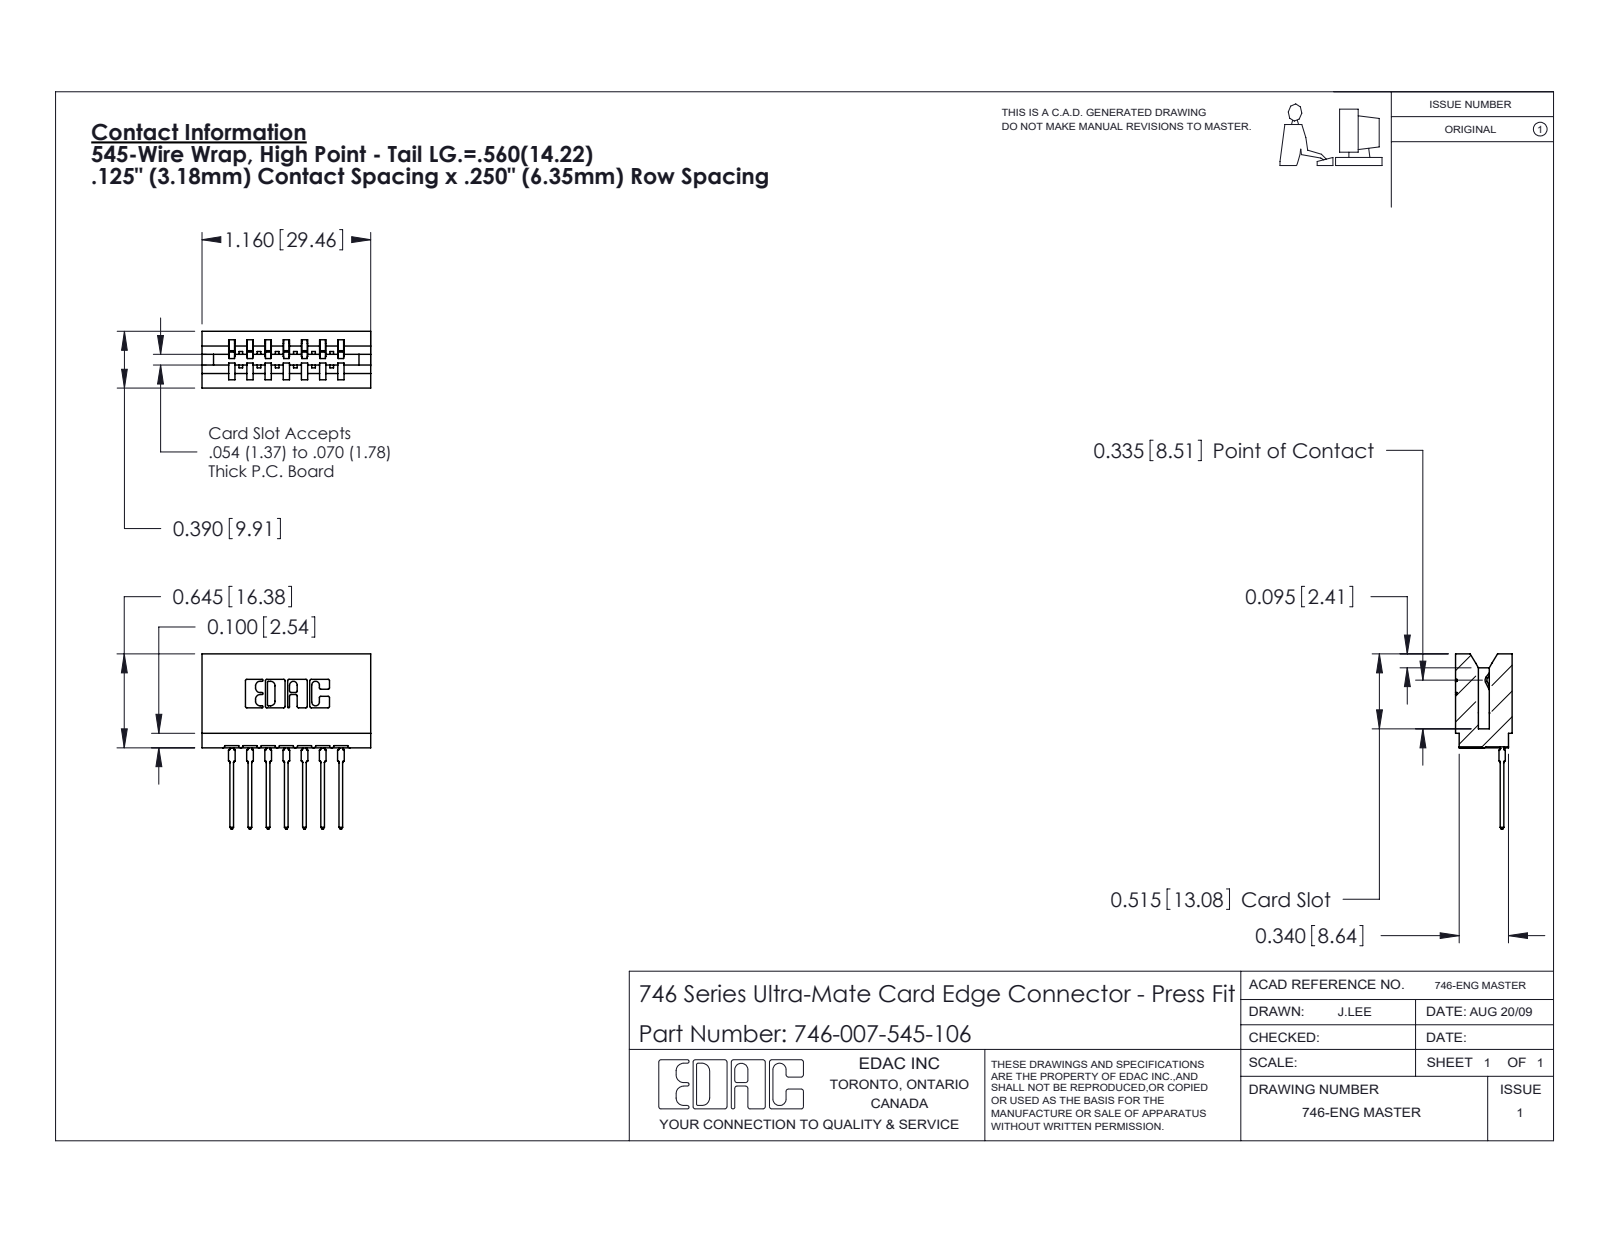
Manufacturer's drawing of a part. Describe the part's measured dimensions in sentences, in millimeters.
The part is named "746-292-001_545; 746-007-545-106; 746 Part_.515 Slot Depth - 06". Its 3-D file was written by "SolidWorks 2020 (CONFIG_CONTROL_DESIGN)". It is 8 solids with 854 faces: 497 planar, 175 cylindrical and 182 other. Overall it measures 30.6 by 29.5 by 9.9 millimeters. Its volume is 3 310 cubic millimeters and its surface area 4 437 square millimeters. Partial cylindrical surfaces (rounded edges, fillets, slot ends): 22 of radius 0.3, 14 of radius 0.5, 8 of radius 0.4, 6 of radius 0.2, 6 of radius 0.8, 4 of radius 0.1, 4 of radius 0.3, 3 of radius 0.7. The main face-to-face distances are 6.4, 1.1, 8.5, 12.7, 3.2, 3.2, 1.4, 5.3, 7.4, 9.9.
